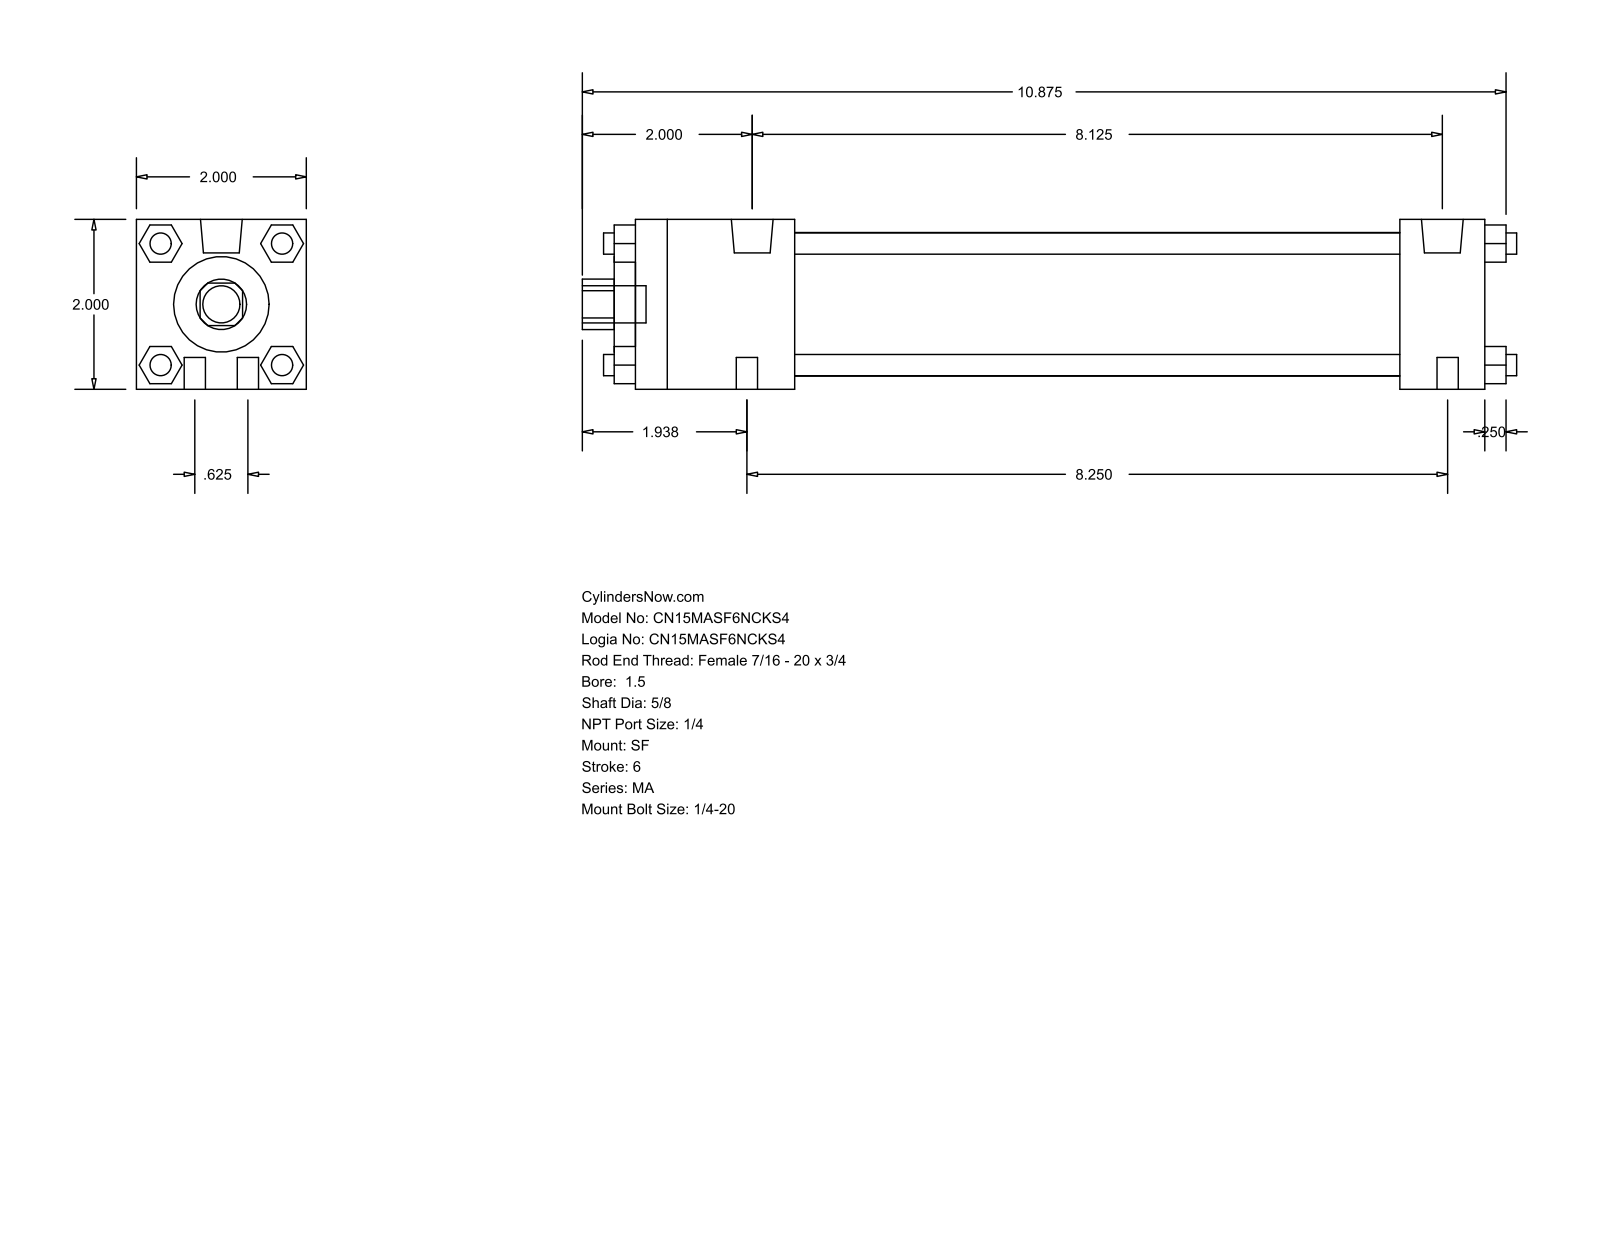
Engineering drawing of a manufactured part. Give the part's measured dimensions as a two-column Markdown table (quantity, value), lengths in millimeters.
| quantity | value |
| --- | --- |
| part name | MA_SF__0150_0.625 |
| STEP written by | GSSL Pune (CONFIG_CONTROL_DESIGN) |
| units | millimeters |
| bodies | 0 solids, 124 faces (94 planar, 30 cylindrical, 0 other) |
| overall size | 279.4 × 50.8 × 50.8 |
| round holes (diameter × count) | 15.88 × 1, 28.57 × 1, 42.93 × 1 |
| round bosses / shafts (diameter × count) | 6.35 × 8, 12.49 × 2, 7.94 × 2, 11.11 × 1 |
| partial cylindrical surfaces (radius × count) | 7.54 × 1 |
| main face-to-face distances | 50.8, 254, 6.35, 260.35, 47.62, 228.59, 180.97, 206.38, 25.41, 53.97 |
